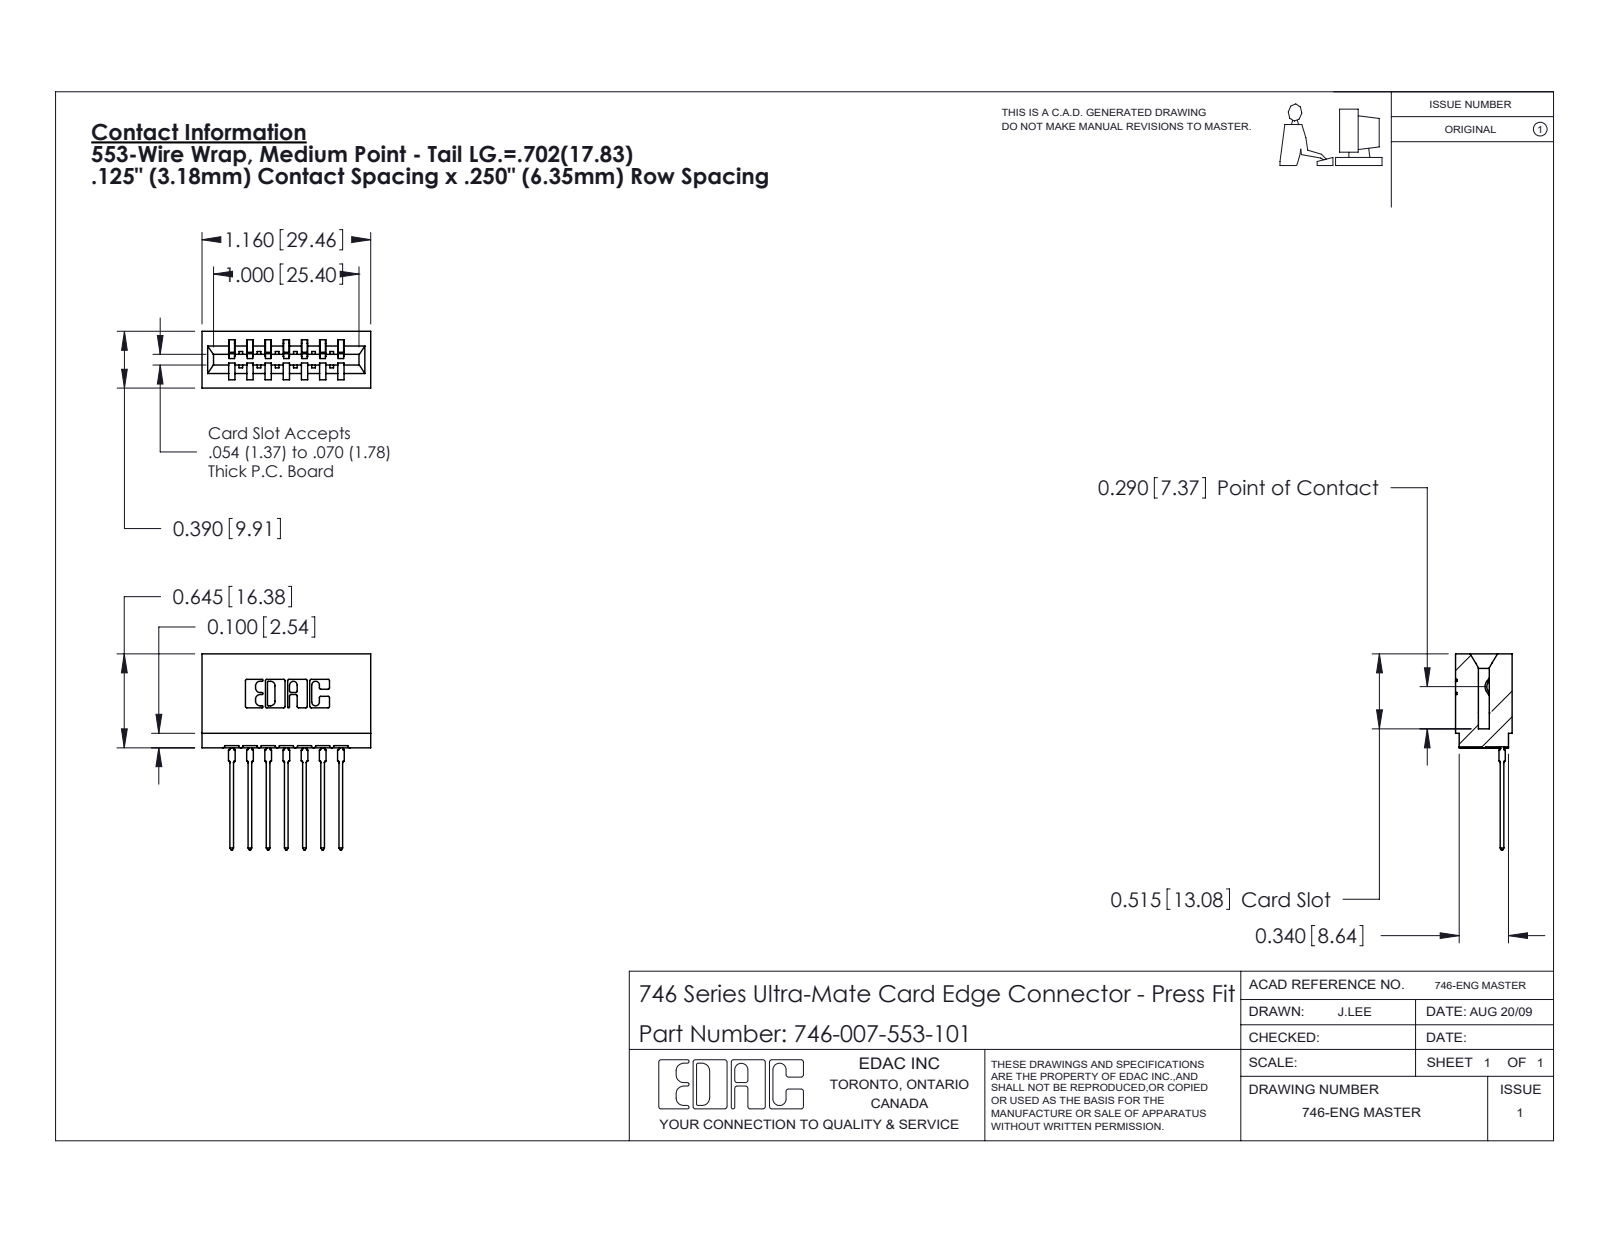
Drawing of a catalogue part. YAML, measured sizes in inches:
part_name: "746-292-001_553; 746-007-553-101; 746 Part_.515 Slot Depth - 01"
step_written_by: "SolidWorks 2020 (CONFIG_CONTROL_DESIGN)"
units: inches
bodies: {solids: 8, faces: 853, planar: 496, cylindrical: 175, other: 182}
overall_size: [1.346, 1.16, 0.39]
volume: 0.204
surface_area: 6.971
partial_cylinders:
  - {radius: 0.01, count: 22}
  - {radius: 0.021, count: 14}
  - {radius: 0.015, count: 8}
  - {radius: 0.007, count: 6}
  - {radius: 0.031, count: 6}
  - {radius: 0.005, count: 4}
  - {radius: 0.011, count: 4}
  - {radius: 0.026, count: 3}
face_to_face_distances: [0.25, 0.042, 0.333, 0.125, 0.057, 0.5, 0.125, 0.292, 0.208, 0.39]
